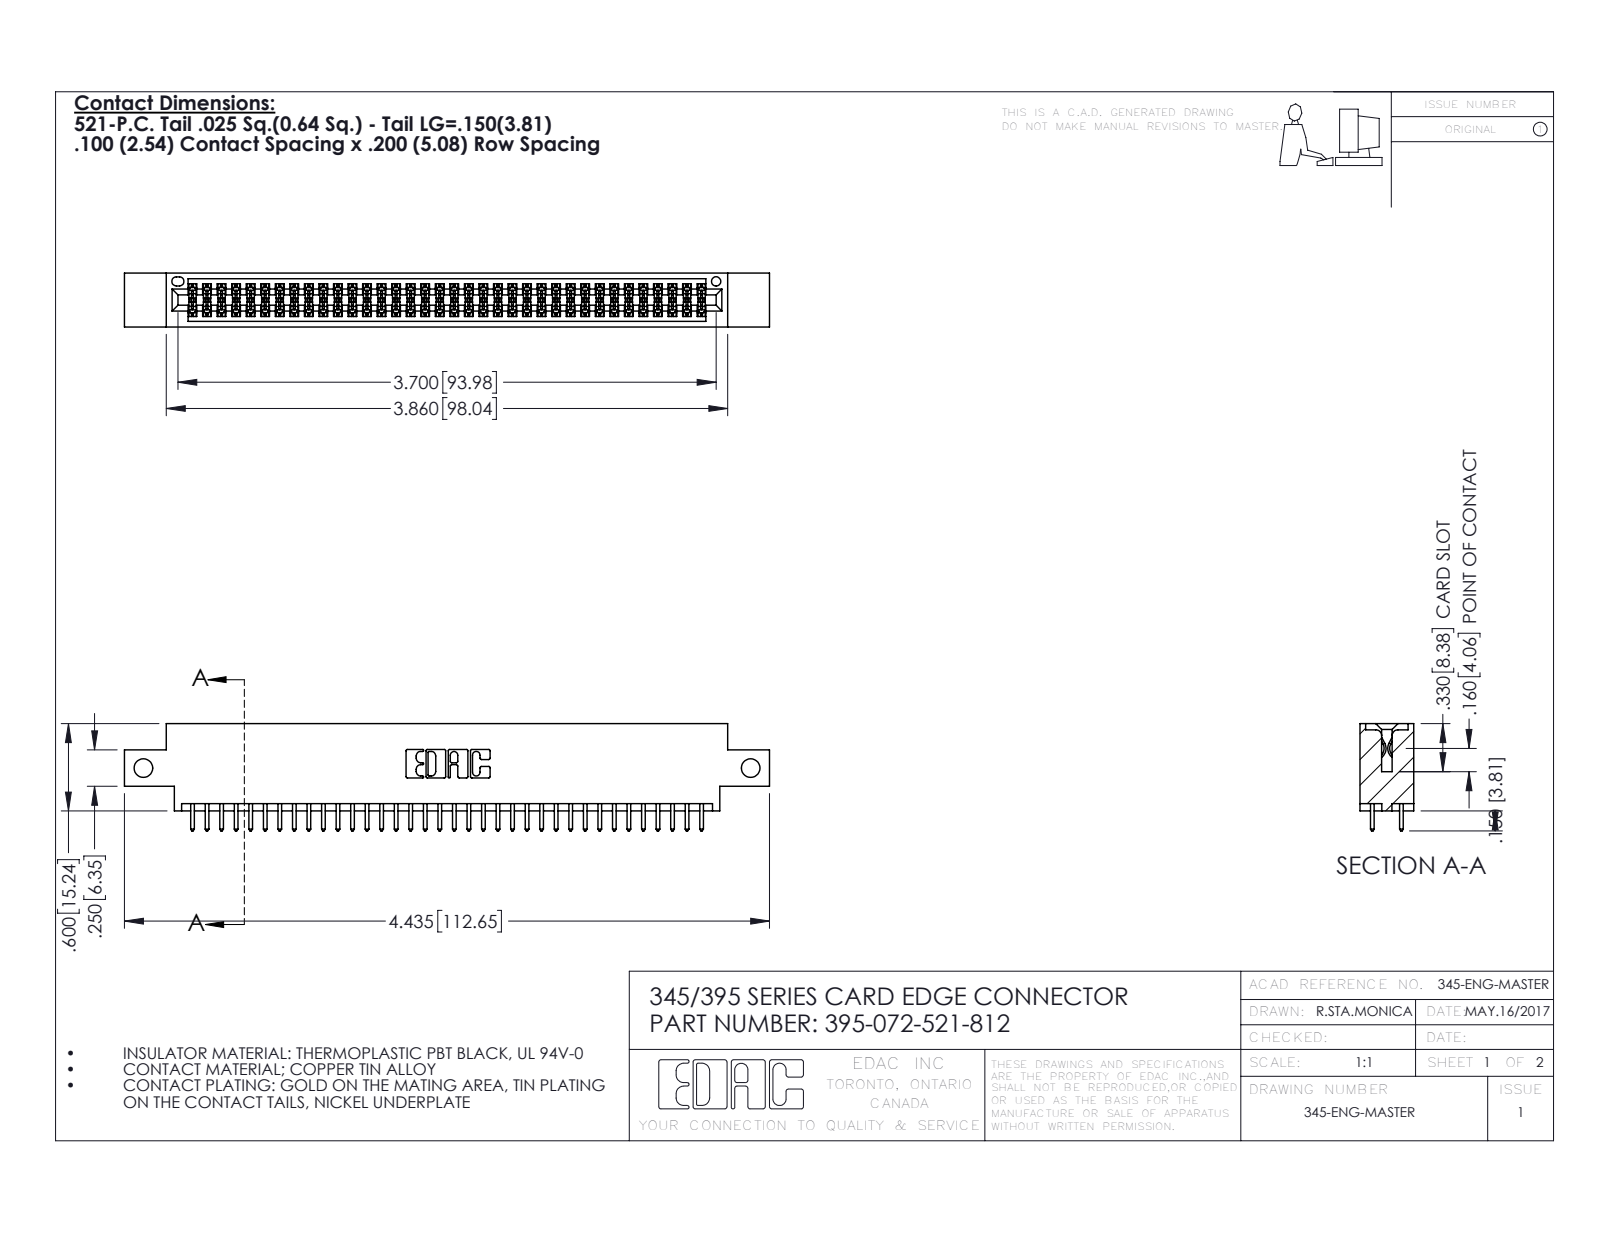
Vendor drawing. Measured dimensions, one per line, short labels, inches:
name: 395-072-521-812; 345-292-001_345-293-121; 345 Part_0.170 Offset - Side Mount
written by: SolidWorks 2016 (CONFIG_CONTROL_DESIGN)
unit: in
bodies: 73 solids, 3730 faces (2460 planar, 1270 cylindrical, 0 other)
size: 4.435 × 0.737 × 0.37
volume: 0.65 in³; area: 23.95 in²
holes: 2× ⌀0.128, 1× ⌀0.064
rounds: 108× R0.006, 72× R0.01, 22× R0.01, 6× R0.007, 6× R0.031, 3× R0.026, 2× R0.014, 2× R0.019
face distances: 0.072, 0.298, 0.37, 0.2, 0.098, 0.272, 0.025, 0.225, 0.175, 0.149
hole spacings: 4.175
